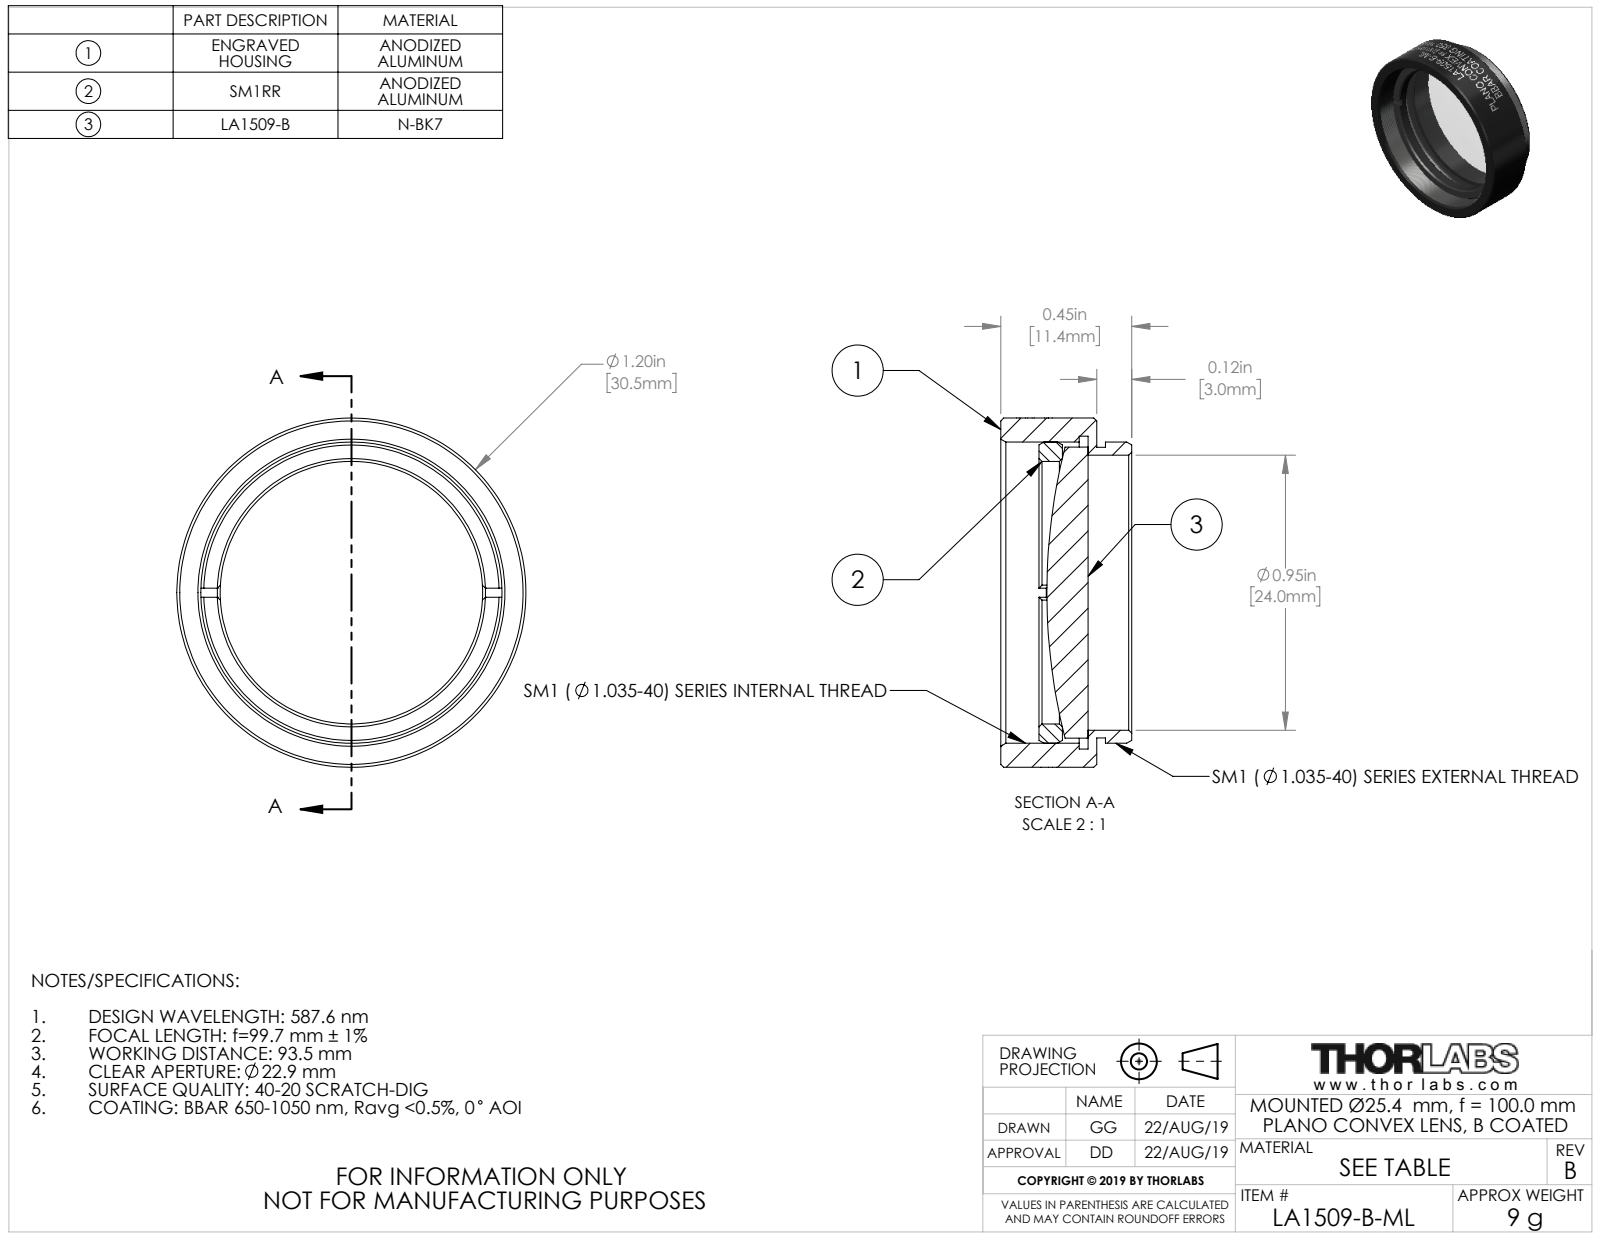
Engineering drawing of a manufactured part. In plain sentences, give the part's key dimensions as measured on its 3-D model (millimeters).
The part is named "24412-E0W". Its 3-D file was written by "SolidWorks 2018 (CONFIG_CONTROL_DESIGN)". It is 3 solids with 156 faces: 20 planar, 112 cylindrical and 24 other. Overall it measures 30.48 by 30.48 by 11.43 millimeters. Its volume is 3 499 cubic millimeters and its surface area 4 320 square millimeters. Round holes: 1 of diameter 22.91, 1 of diameter 24, 1 of diameter 27.3. Round bosses or shafts: 1 of diameter 30.48, 1 of diameter 26.29, 1 of diameter 25.4, 1 of diameter 25.37. The main face-to-face distances are 0.76, 8.38, 7.62, 3, 2.24, 5.38, 5.03, 4.27, 2.03, 3.35.
